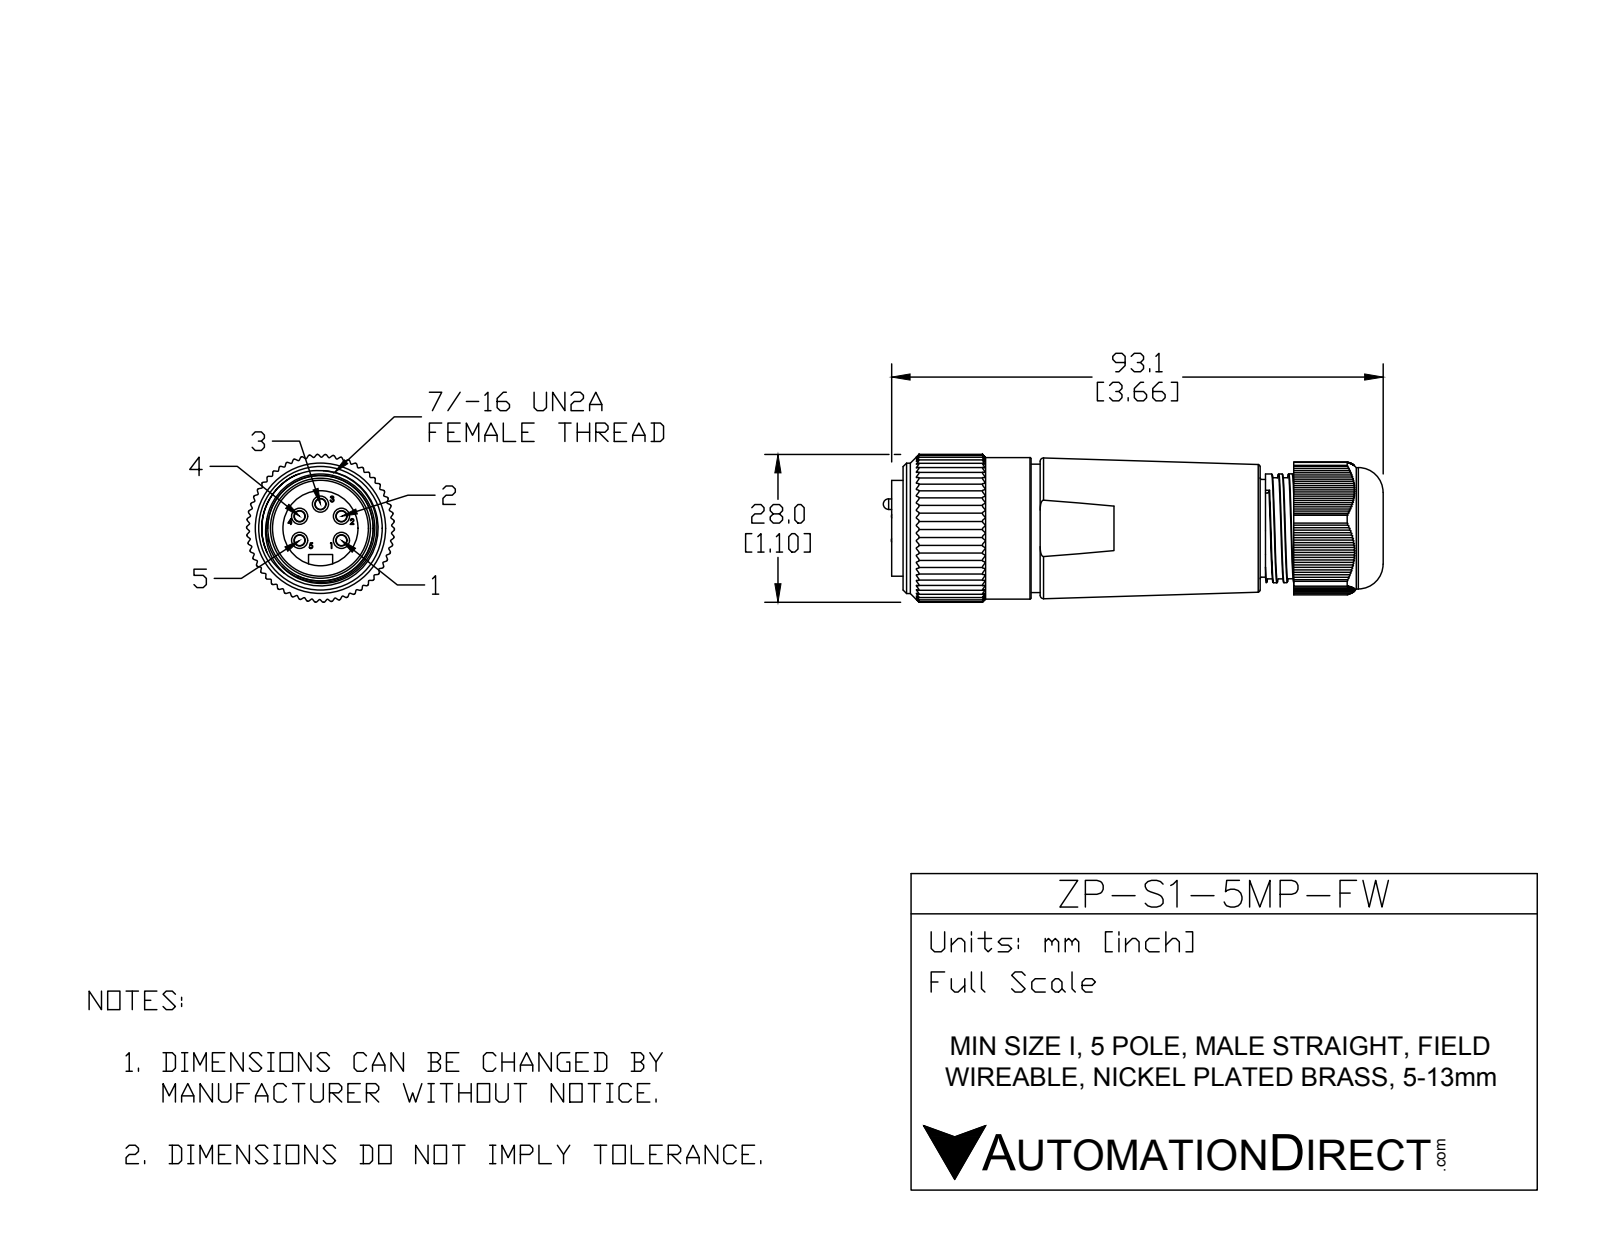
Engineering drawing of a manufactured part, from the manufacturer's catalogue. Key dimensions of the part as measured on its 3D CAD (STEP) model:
Part name (STEP PRODUCT): ZP-S1-5MP-FW
STEP written by: SolidWorks 2015 (AUTOMOTIVE_DESIGN)
Units: millimetres
Bodies: 9 solids, 850 faces (461 planar, 314 cylindrical, 75 other)
Overall size (bounding box): 95.14 × 27.99 × 27.98
Volume: 41 937 mm³ · Surface area: 15 072 mm²
Round holes (diameter × count): ⌀3.56 ×1, ⌀13.46 ×1, ⌀14.22 ×1, ⌀20.58 ×1, ⌀21.57 ×1, ⌀24.2 ×1, ⌀25.4 ×1
Round bosses / shafts (diameter × count): ⌀3.15 ×5, ⌀2 ×5, ⌀26.8 ×1, ⌀24.68 ×1, ⌀24.3 ×1, ⌀22.99 ×1, ⌀20.6 ×1, ⌀18.14 ×1
Partial cylindrical surfaces — rounded edges, fillets, slot ends (radius × count): R0.25 ×165, R2.29 ×1, R13.23 ×1, R14 ×1
Main face-to-face distances: 69.12, 1.06, 0.35, 0.71, 70.28, 6.35, 8.79, 60.33, 1.41, 2.12
